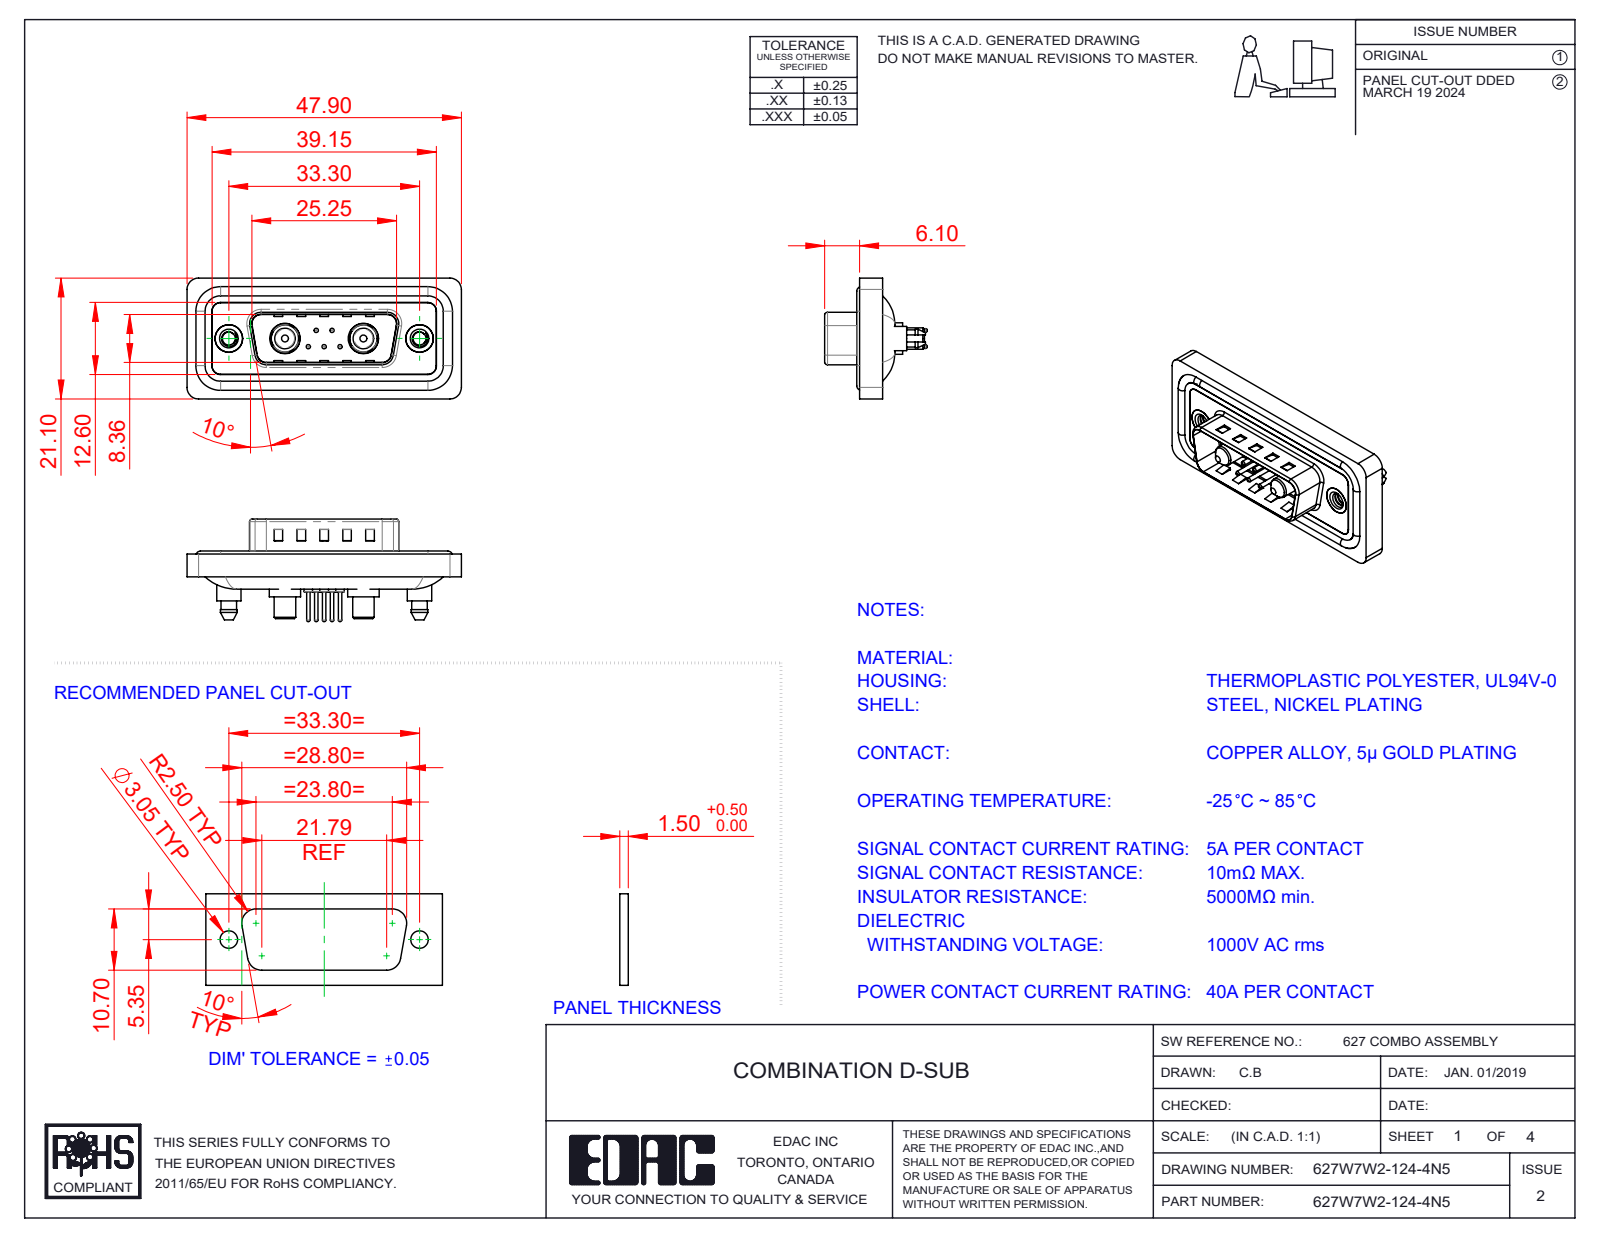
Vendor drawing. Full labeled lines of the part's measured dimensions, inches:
Part name (STEP PRODUCT): 627Combo Contact Row 1_24; Power Pin_40A S; 627W7W2-124-4N5; 627Combo Housing_7W2 (+5 more)
STEP written by: SolidWorks 2023 (CONFIG_CONTROL_DESIGN)
Units: inches
Bodies: 16 solids, 760 faces (248 planar, 324 cylindrical, 188 other)
Overall size (bounding box): 1.886 × 0.831 × 0.705
Volume: 0.347 in³ · Surface area: 14.18 in²
Round holes (diameter × count): ⌀0.03 ×5, ⌀0.063 ×5, ⌀0.079 ×5, ⌀0.089 ×2, ⌀0.157 ×2, ⌀0.189 ×2, ⌀0.191 ×2, ⌀0.197 ×2, ⌀0.209 ×2
Round bosses / shafts (diameter × count): ⌀0.059 ×5, ⌀0.024 ×5, ⌀0.063 ×4, ⌀0.217 ×2, ⌀0.213 ×2, ⌀0.205 ×2, ⌀0.193 ×2, ⌀0.187 ×2
Partial cylindrical surfaces — rounded edges, fillets, slot ends (radius × count): R0.059 ×28, R0.079 ×20, R0.063 ×10, R0.02 ×8, R0.01 ×4, R0.024 ×4, R0.026 ×4, R0.035 ×4
Main face-to-face distances: 0.016, 0.043, 0.063, 0.059, 0.122, 0.02, 0.114, 0.028, 0.032, 0.377
Hole centre spacings: 0.124, 0.109, 0.386, 0.925, 0.17, 0.17, 0.198, 0.198
